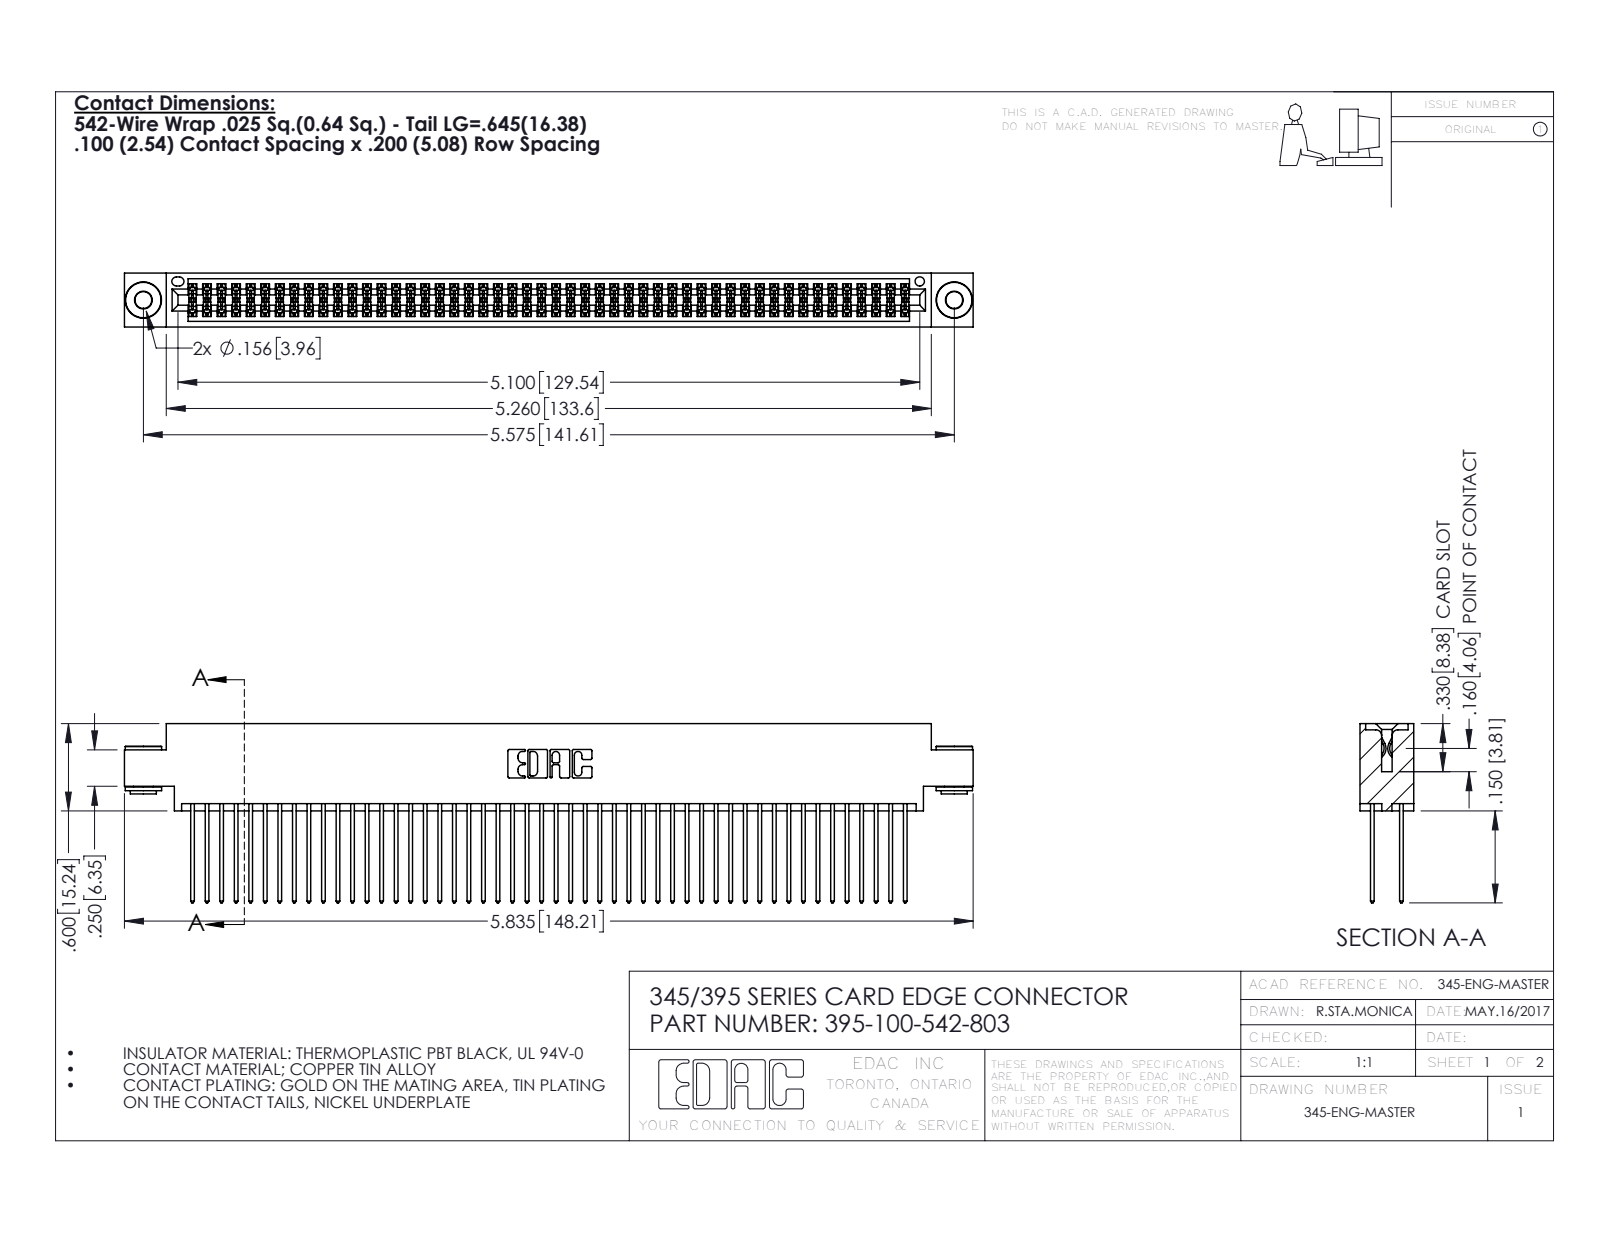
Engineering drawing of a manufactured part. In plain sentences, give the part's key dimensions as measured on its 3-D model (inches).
The part is named "395-100-542-803; 345 Part_0.170 Offset - 0.156 Dia-TH; 345-250-002_345-250-002-102; 345-292-001_345-293-142". Its 3-D file was written by "SolidWorks 2016 (CONFIG_CONTROL_DESIGN)". It is 103 solids with 5168 faces: 3394 planar, 1766 cylindrical and 8 other. Overall it measures 5.835 by 1.232 by 0.37 inches. Its volume is 0.906 cubic inches and its surface area 38.17 square inches. Round holes: 2 of diameter 0.116, 2 of diameter 0.156, 1 of diameter 0.064. Round bosses or shafts: 2 of diameter 0.25, 2 of diameter 0.18, 2 of diameter 0.136. Partial cylindrical surfaces (rounded edges, fillets, slot ends): 150 of radius 0.006, 100 of radius 0.01, 22 of radius 0.01, 6 of radius 0.007, 6 of radius 0.031, 3 of radius 0.026, 2 of radius 0.014, 2 of radius 0.019. The main face-to-face distances are 0.072, 0.298, 0.2, 0.098, 0.272, 0.025, 0.37, 0.225, 0.175, 0.149. The hole center spacings are 0.27, 5.339, 5.575.
